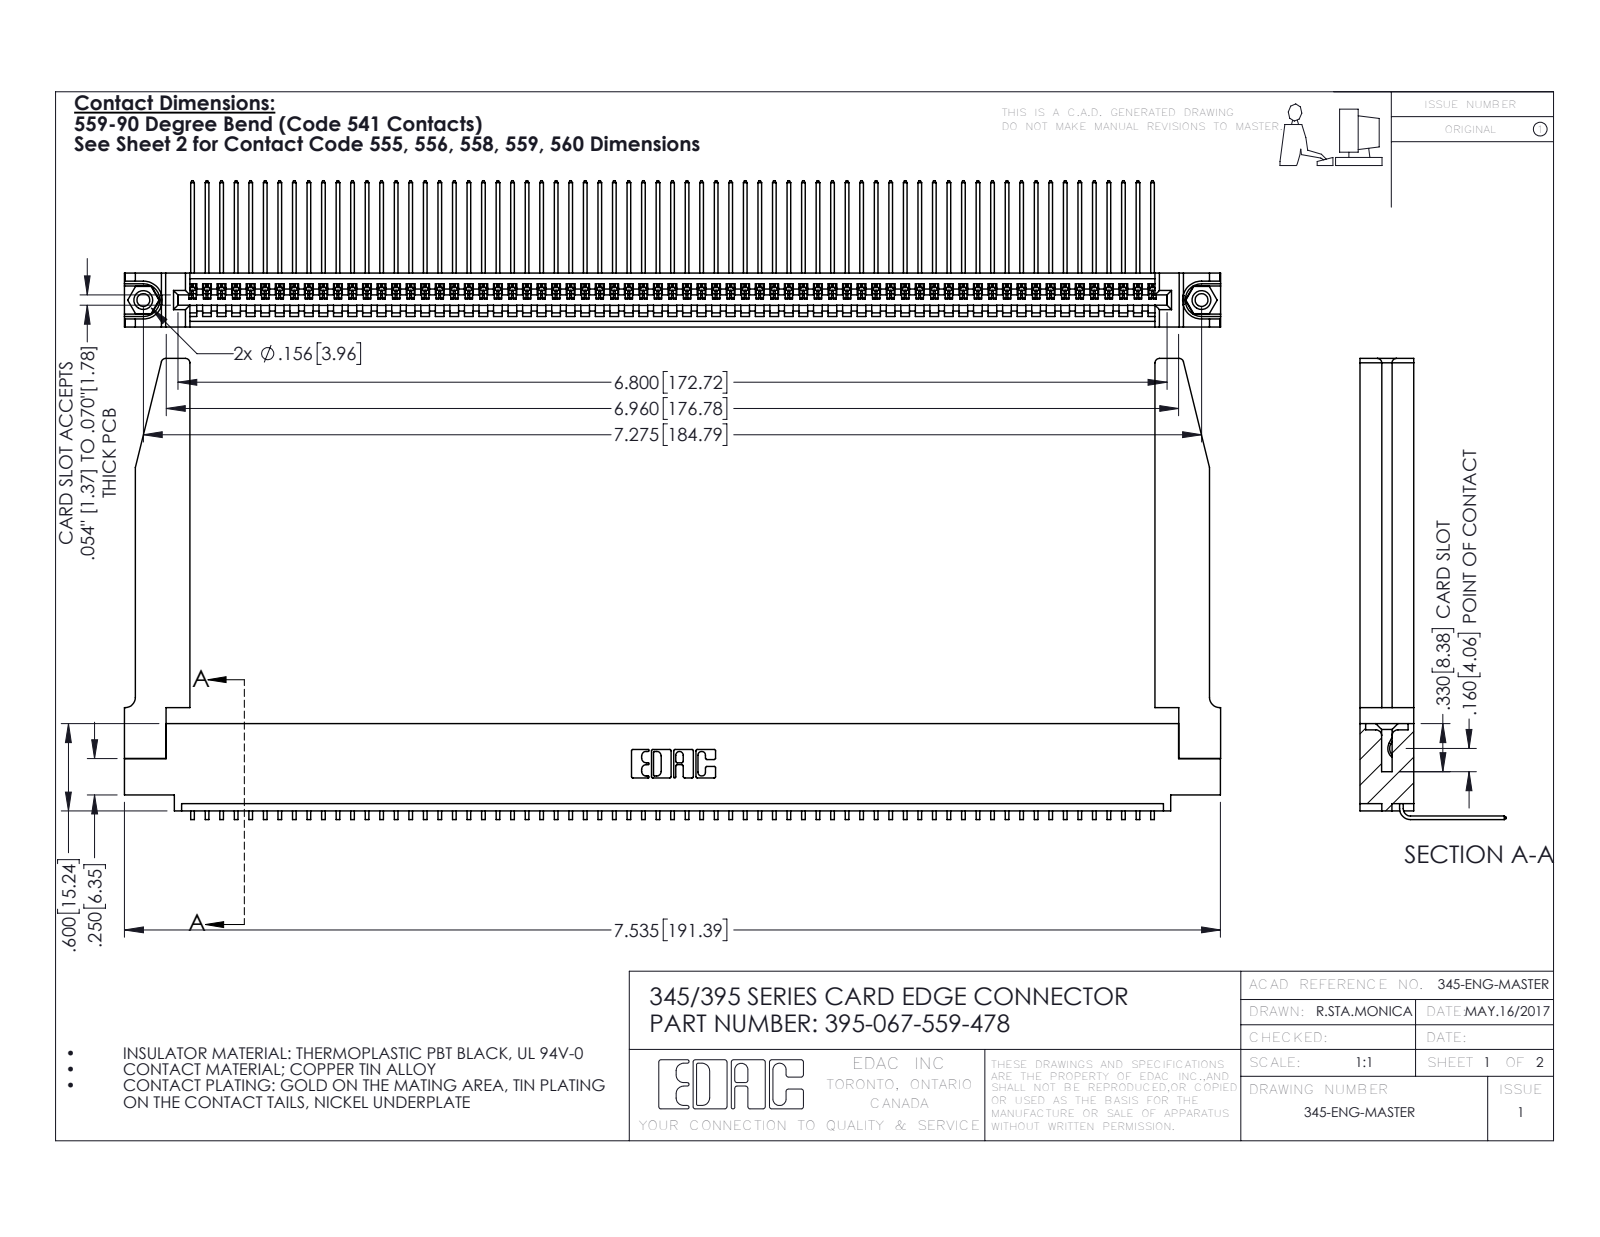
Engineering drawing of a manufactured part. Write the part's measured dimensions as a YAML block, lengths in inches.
part_name: "345 Part_0.110 Offset - 0.156 Dia-TH; 395-067-559-478; 345-220-078_345-220-078; 345-250-001_345-250-001-102 (+1 more)"
step_written_by: "SolidWorks 2016 (CONFIG_CONTROL_DESIGN)"
units: inches
bodies: {solids: 72, faces: 4384, planar: 3040, cylindrical: 1292, other: 52}
overall_size: [7.536, 3.169, 1.005]
volume: 1.605
surface_area: 51.48
round_holes:
  - {diameter: 0.089, count: 2}
  - {diameter: 0.125, count: 2}
  - {diameter: 0.156, count: 2}
  - {diameter: 0.064, count: 1}
round_bosses_or_shafts:
  - {diameter: 0.155, count: 2}
partial_cylinders:
  - {radius: 0.006, count: 134}
  - {radius: 0.01, count: 22}
  - {radius: 0.03, count: 8}
  - {radius: 0.007, count: 6}
  - {radius: 0.031, count: 6}
  - {radius: 0.026, count: 3}
  - {radius: 0.031, count: 2}
  - {radius: 0.04, count: 2}
face_to_face_distances: [0.37, 0.072, 0.298, 0.098, 0.272, 0.025, 0.2, 0.225, 0.149, 0.148]
hole_center_spacings: [0.27, 7.039, 7.275]
